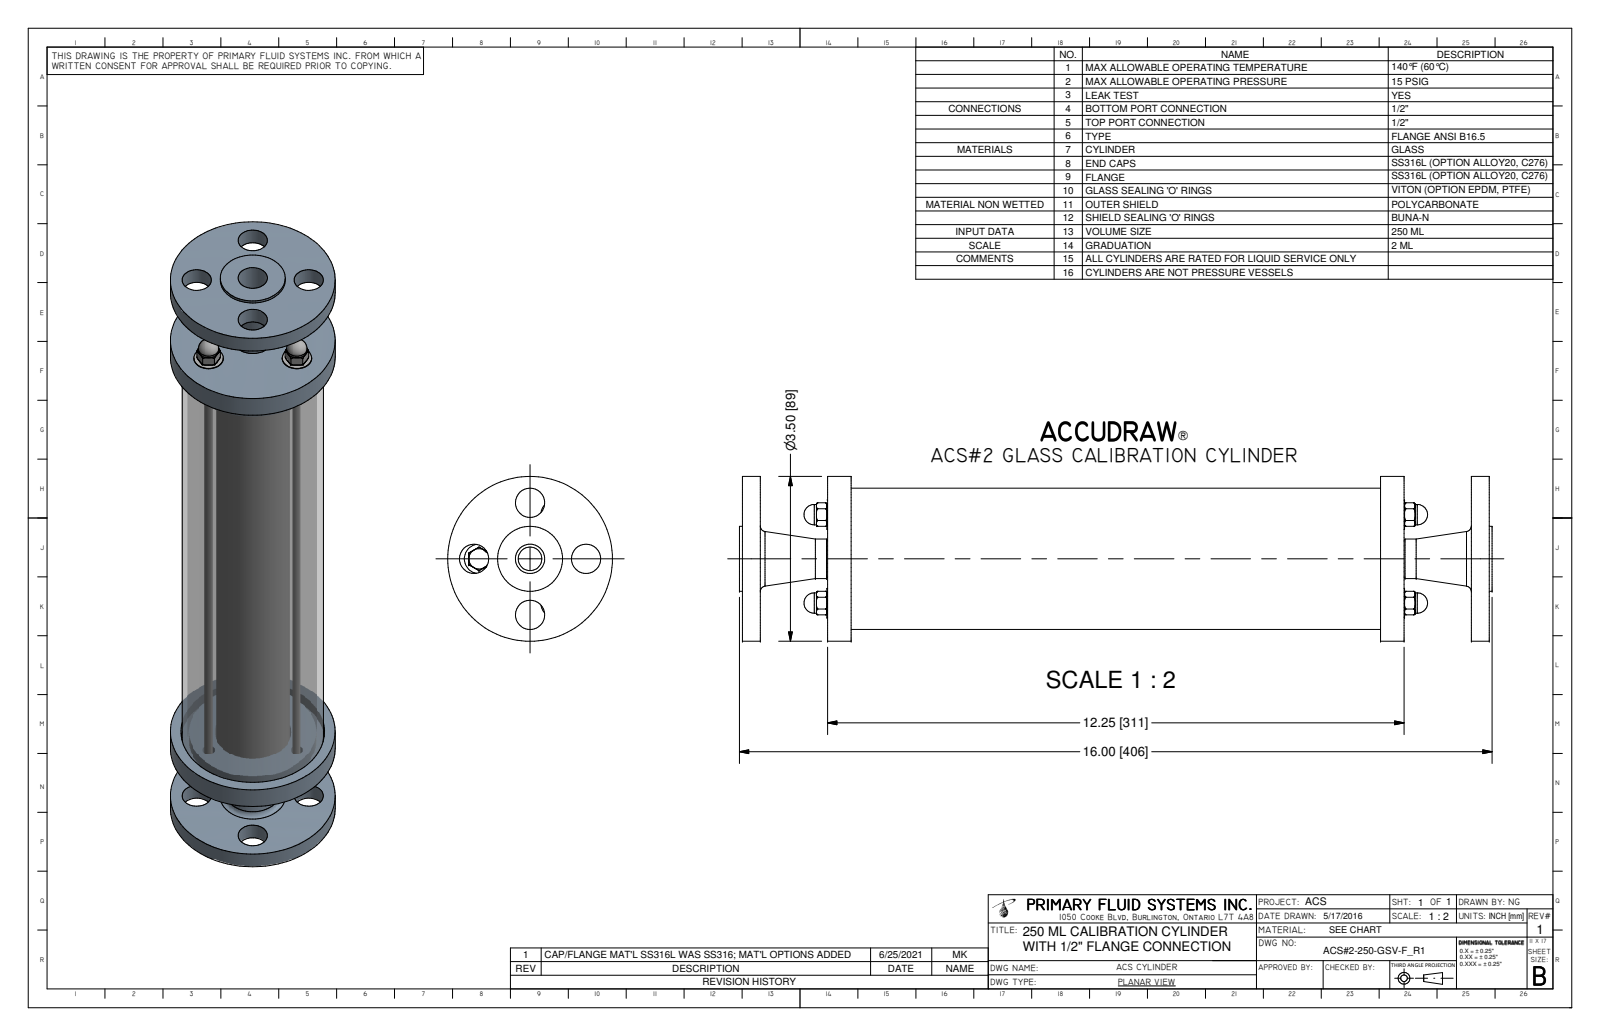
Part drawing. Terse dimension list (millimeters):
name: ACS#2-250-GSV-F_R0; ACS-3-250-METAL-S_R1; ACS-2-250-PC_R6; ACS-1-250-A_R0 (+4 more)
written by: Autodesk Inventor 2009 (AUTOMOTIVE_DESIGN)
unit: mm
bodies: 21 solids, 455 faces (46 planar, 57 cylindrical, 352 other)
size: 406.3 × 88.9 × 88.9
volume: 564 500 mm³; area: 314 800 mm²
holes: 4× ⌀15.7, 3× ⌀4.6, 3× ⌀6.8, 3× ⌀7.1, 1× ⌀15.8, 1× ⌀36, 1× ⌀41.5, 1× ⌀69.9, 1× ⌀77.5
bosses: 3× ⌀15.9, 3× ⌀4.7, 1× ⌀88.9, 1× ⌀76.2, 1× ⌀68.6, 1× ⌀40, 1× ⌀35.1, 1× ⌀34.7
face distances: 46, 357.1, 9.7, 393.4, 36.3, 347.5, 58.7, 344.4, 49, 334.8
hole spacings: 30.2, 42.7, 27.5, 15.2, 29, 40.9, 47.7, 50
